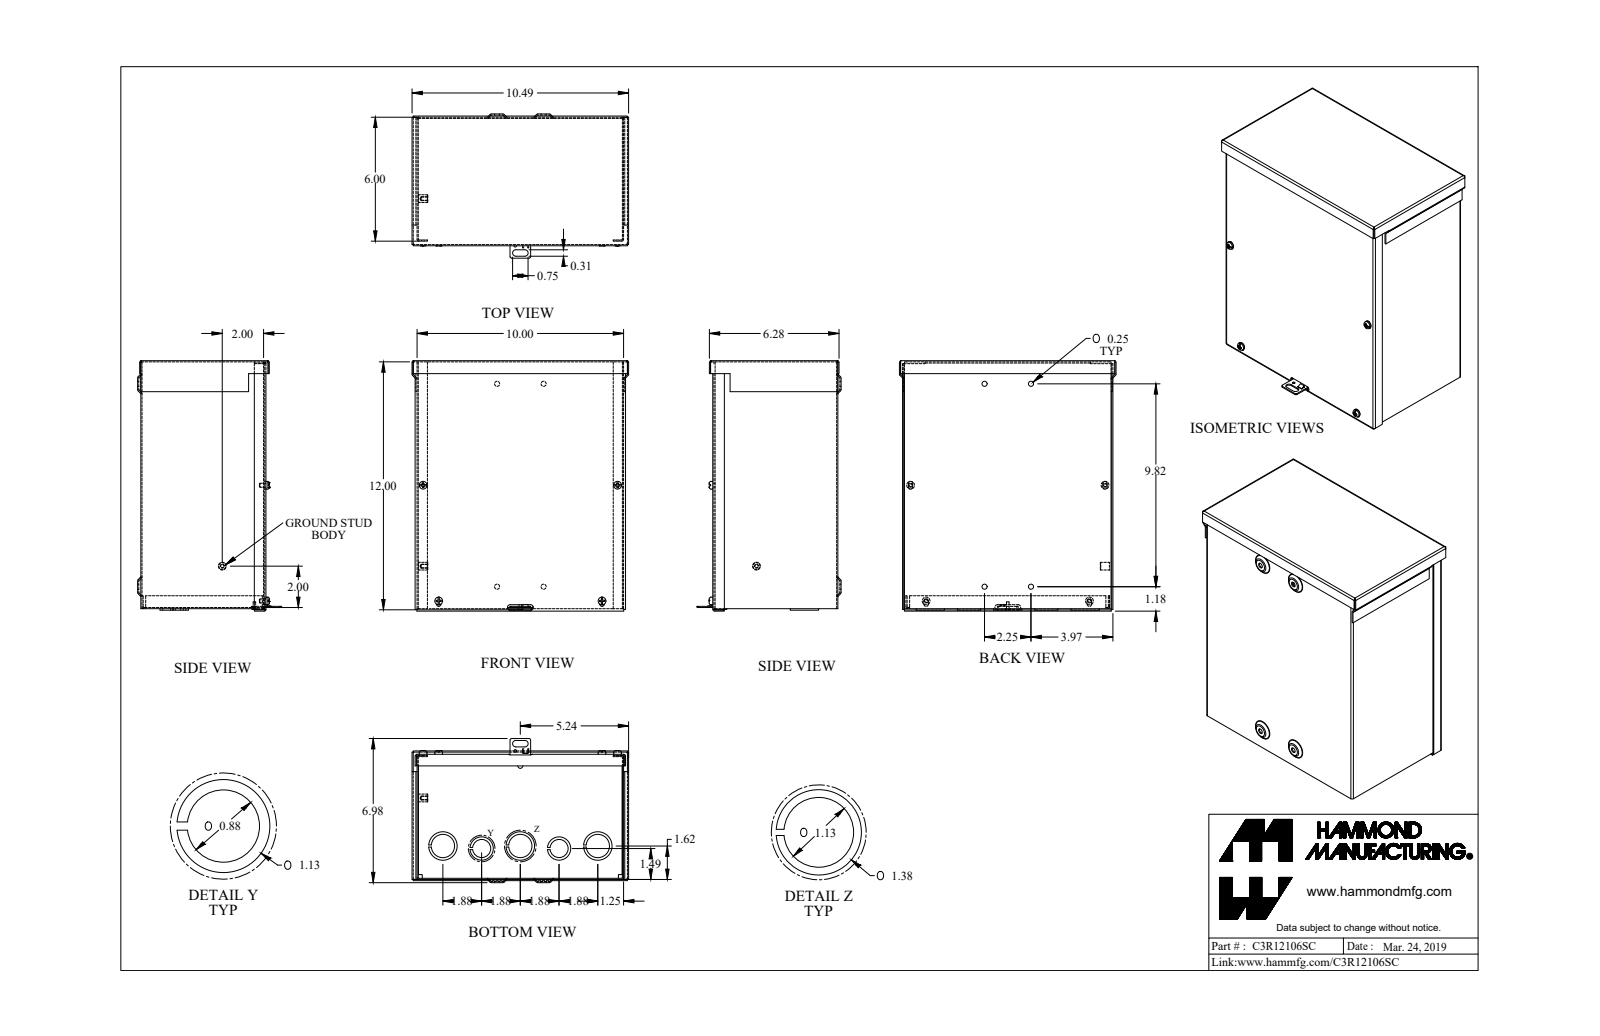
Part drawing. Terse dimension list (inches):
name: C3R12106SC_Default
written by: SolidWorks 2019 (CONFIG_CONTROL_DESIGN)
unit: in
bodies: 11 solids, 429 faces (226 planar, 117 cylindrical, 86 other)
size: 12.12 × 10.489 × 6.977
volume: 33.42 in³; area: 1 181 in²
holes: 4× ⌀0.17, 4× ⌀0.25, 3× ⌀1.125, 2× ⌀0.875, 1× ⌀0.125, 1× ⌀0.137, 1× ⌀0.156
bosses: 4× ⌀0.375, 4× ⌀0.19, 2× ⌀1.375, 2× ⌀1.125, 1× ⌀1.375, 1× ⌀0.375, 1× ⌀0.125
rounds: 21× R0.029, 21× R0.086, 8× R0.125, 4× R0.106, 4× R0.109, 2× R0.156
face distances: 0.057, 6, 9.943, 5.943, 6.057, 0.057, 10, 9.886, 11.886, 11.943
hole spacings: 6.077, 7.623, 3.75, 1.879, 1.88, 2.25, 2.946, 5.152
